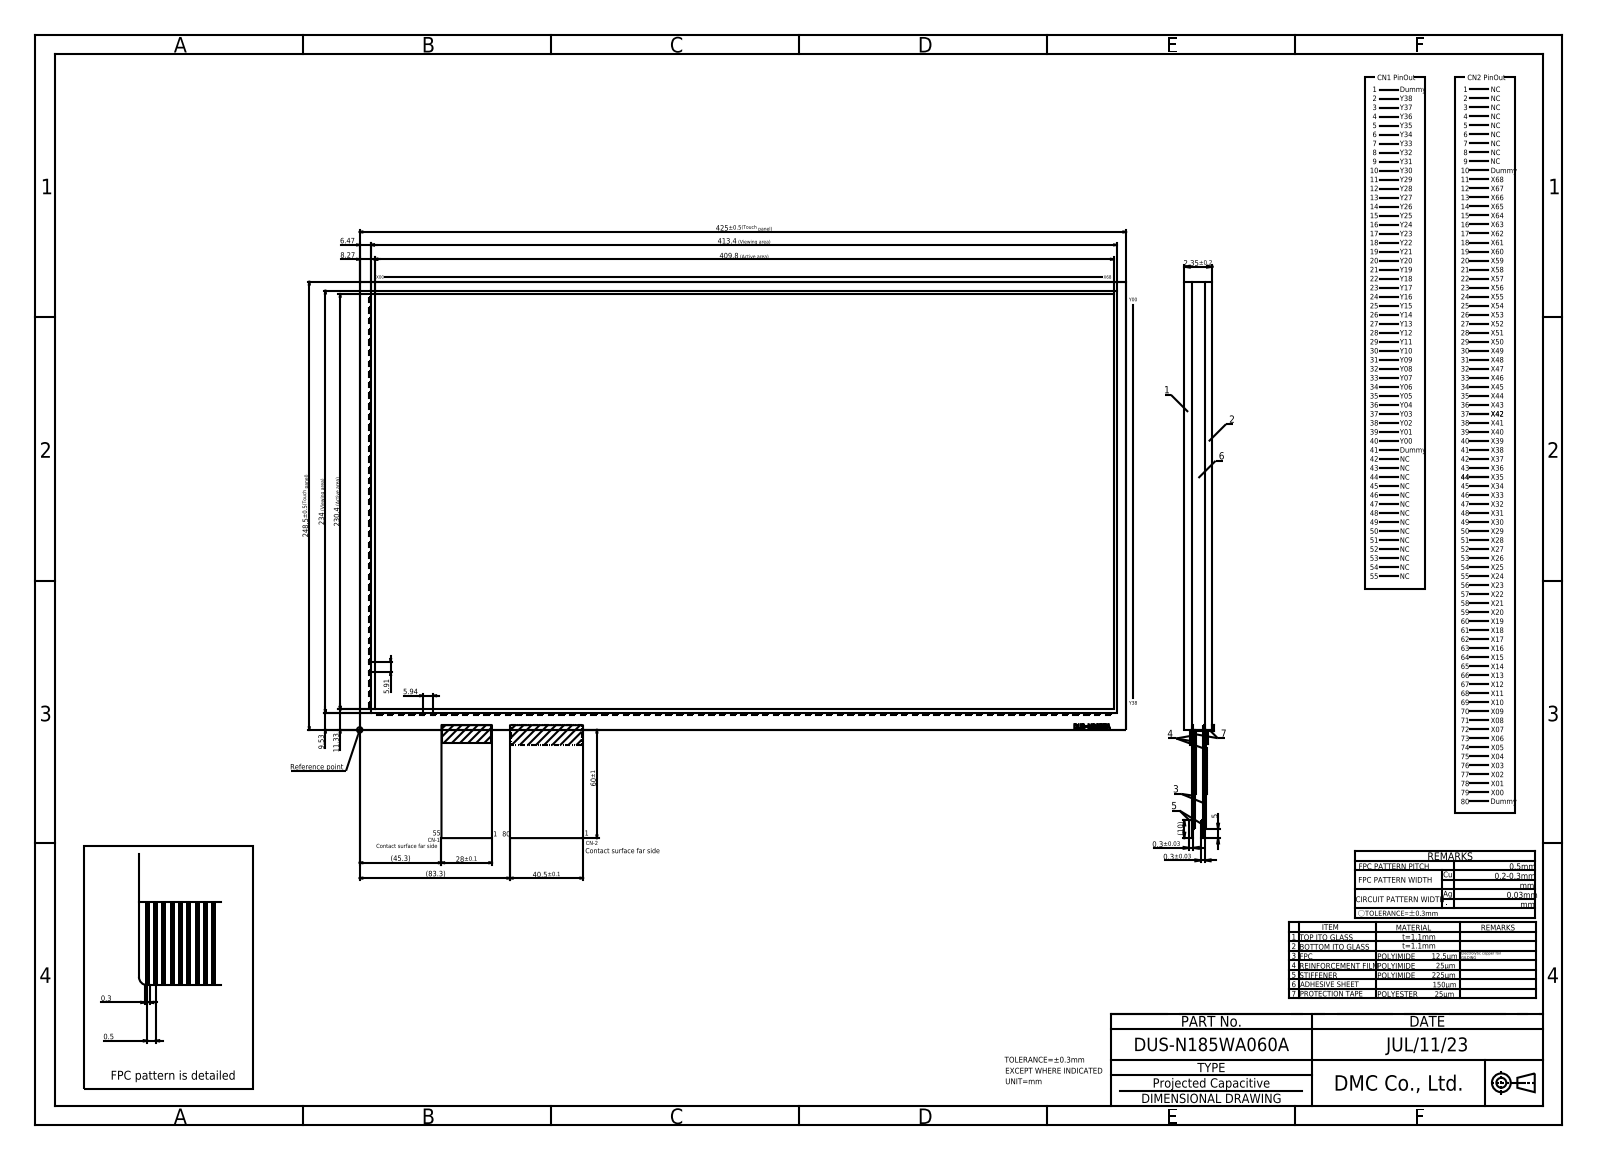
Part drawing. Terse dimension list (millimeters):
name: DUS-N185WA060A
written by: Autodesk Inventor 2020 (CONFIG_CONTROL_DESIGN)
unit: mm
bodies: 1 solid, 578 faces (574 planar, 4 cylindrical, 0 other)
size: 595 × 358.2 × 2.35
volume: 248 538 mm³; area: 222 956 mm²
rounds: 4× R0.2
face distances: 2.35, 1.1, 1.2, 1.15, 1.25, 1, 2.25, 248.5, 0.8, 0.7
